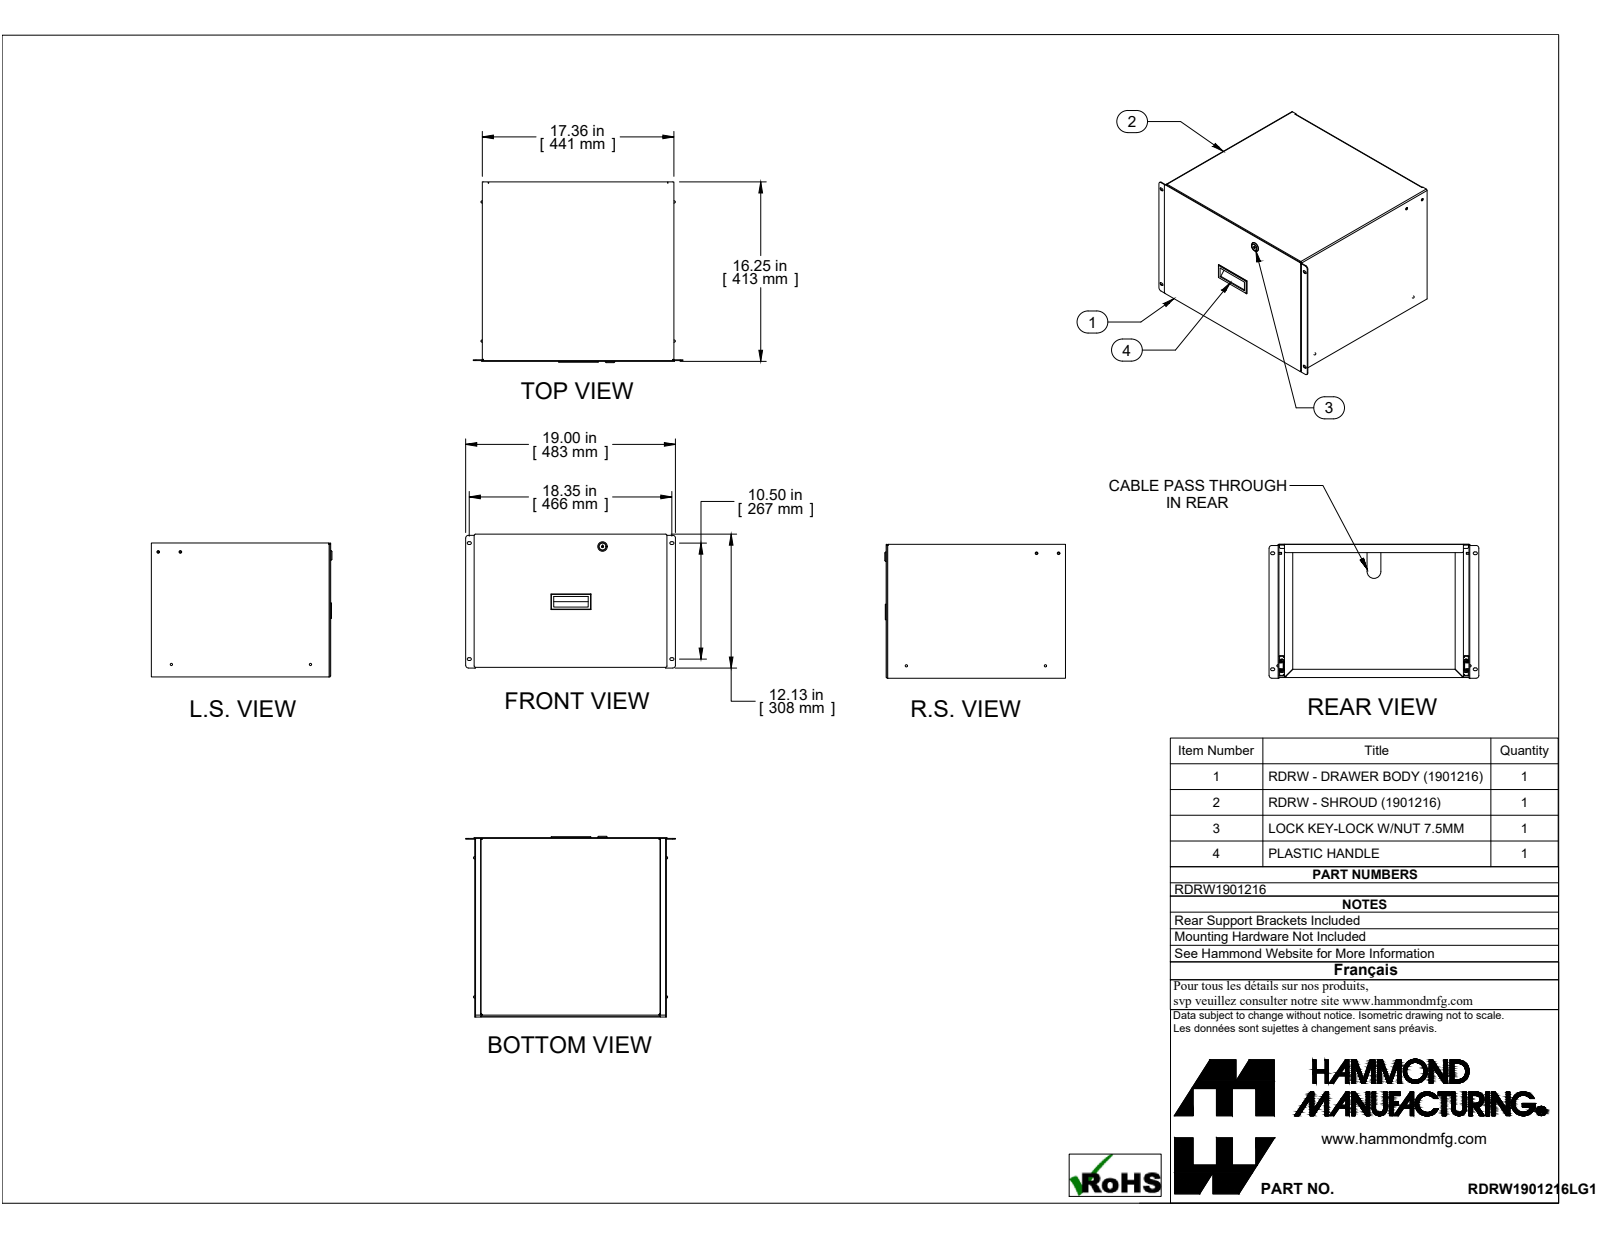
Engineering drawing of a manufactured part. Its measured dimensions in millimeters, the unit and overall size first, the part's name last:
Units: millimetres
Overall size (bounding box): 482.6 × 415.6 × 308
Round holes (diameter × count): ⌀4.5 ×6, ⌀4 ×4, ⌀4.6 ×4, ⌀6.4 ×4, ⌀4.4 ×3, ⌀4.1 ×2, ⌀3.9 ×1, ⌀5 ×1
Round bosses / shafts (diameter × count): ⌀6 ×2, ⌀4.2 ×2, ⌀22 ×1, ⌀15.9 ×1, ⌀13.9 ×1, ⌀8.5 ×1
Partial cylindrical surfaces — rounded edges, fillets, slot ends (radius × count): R2.2 ×52, R0.7 ×40, R1.3 ×16, R3.2 ×16, R0.6 ×8, R1.8 ×8, R0.9 ×6, R2.5 ×6
Main face-to-face distances: 1.8, 1.2, 424.5, 12.7, 14.5, 426.3, 439, 15.7, 425.1, 13.9
Hole centre spacings: 9.7, 320, 9.1, 15.8, 18.8, 25.5, 32, 34.6
Volume: 1 944 000 mm³ · Surface area: 2 561 000 mm²
Bodies: 24 solids, 682 faces (376 planar, 264 cylindrical, 42 other)
Part name (STEP PRODUCT): RDRW1901216LG1
STEP written by: SolidWorks 2019 (CONFIG_CONTROL_DESIGN)
